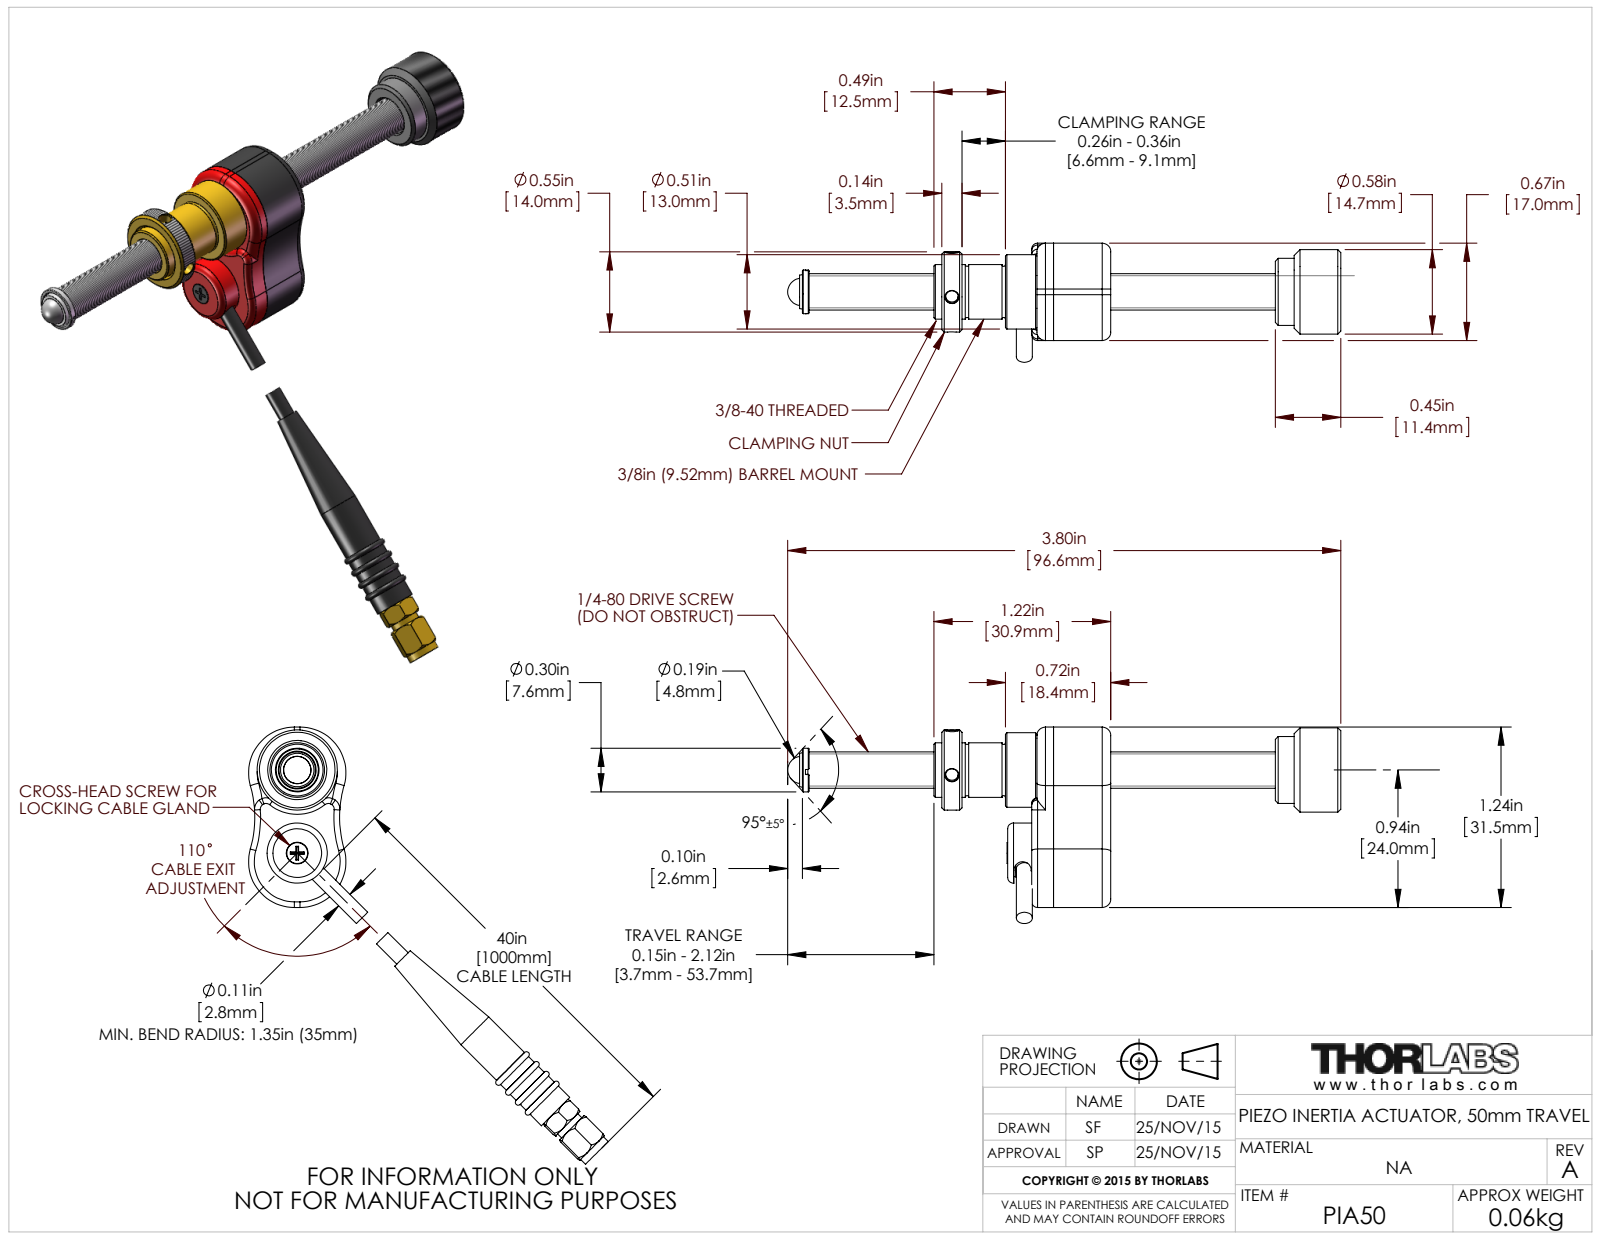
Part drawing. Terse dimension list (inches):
name: PIA50
written by: SolidWorks 2014 (CONFIG_CONTROL_DESIGN)
unit: in
bodies: 14 solids, 1041 faces (524 planar, 204 cylindrical, 313 other)
size: 3.802 × 3.004 × 2.473
volume: 0.531 in³; area: 16.93 in²
holes: 4× ⌀0.087, 3× ⌀0.049, 3× ⌀0.071, 2× ⌀0.122, 2× ⌀0.268, 1× ⌀0.018, 1× ⌀0.031, 1× ⌀0.08, 1× ⌀0.083, 1× ⌀0.11, 1× ⌀0.118, 1× ⌀0.134
bosses: 1× ⌀0.58, 1× ⌀0.551, 1× ⌀0.512, 1× ⌀0.46, 1× ⌀0.413, 1× ⌀0.375, 1× ⌀0.327, 1× ⌀0.3
rounds: 13× R0.039, 6× R0.059, 6× R0.079, 4× R0.276, 4× R0.283, 4× R0.299, 4× R0.303, 4× R0.315
face distances: 0.031, 0.508, 0.402, 0.433, 0.075, 0.476, 0.035, 0.11, 0.543, 0.165
hole spacings: 0.197, 0.341, 0.502, 0.748, 0.15, 0.205, 0.214, 0.248
